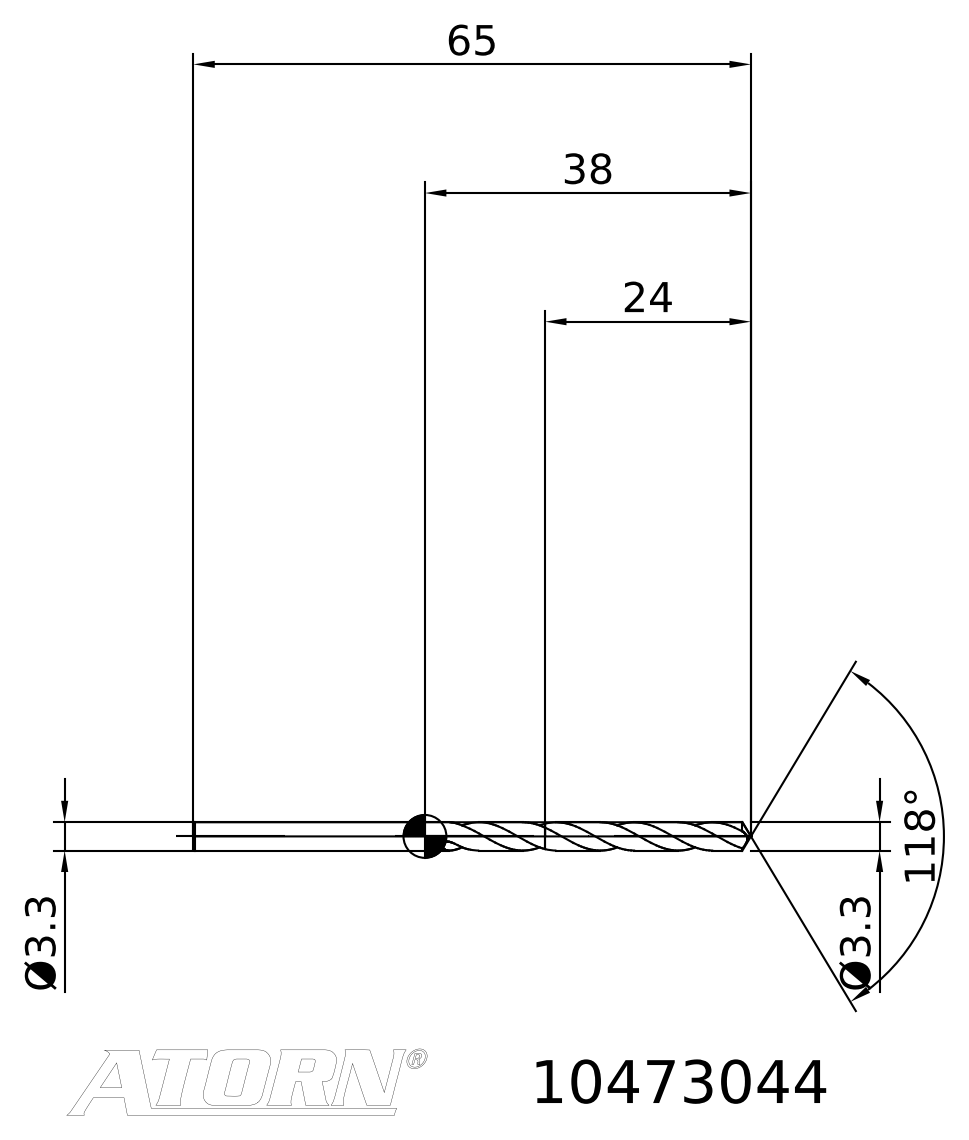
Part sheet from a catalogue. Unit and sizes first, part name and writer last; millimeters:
Units: millimetres
Overall size (bounding box): 65 × 5.02 × 3.3
Main face-to-face distances: 41
Volume: 448 mm³ · Surface area: 726 mm²
Bodies: 2 solids, 26 faces (3 planar, 0 cylindrical, 23 other)
STEP written by: TDM (AUTOMOTIVE_DESIGN)
